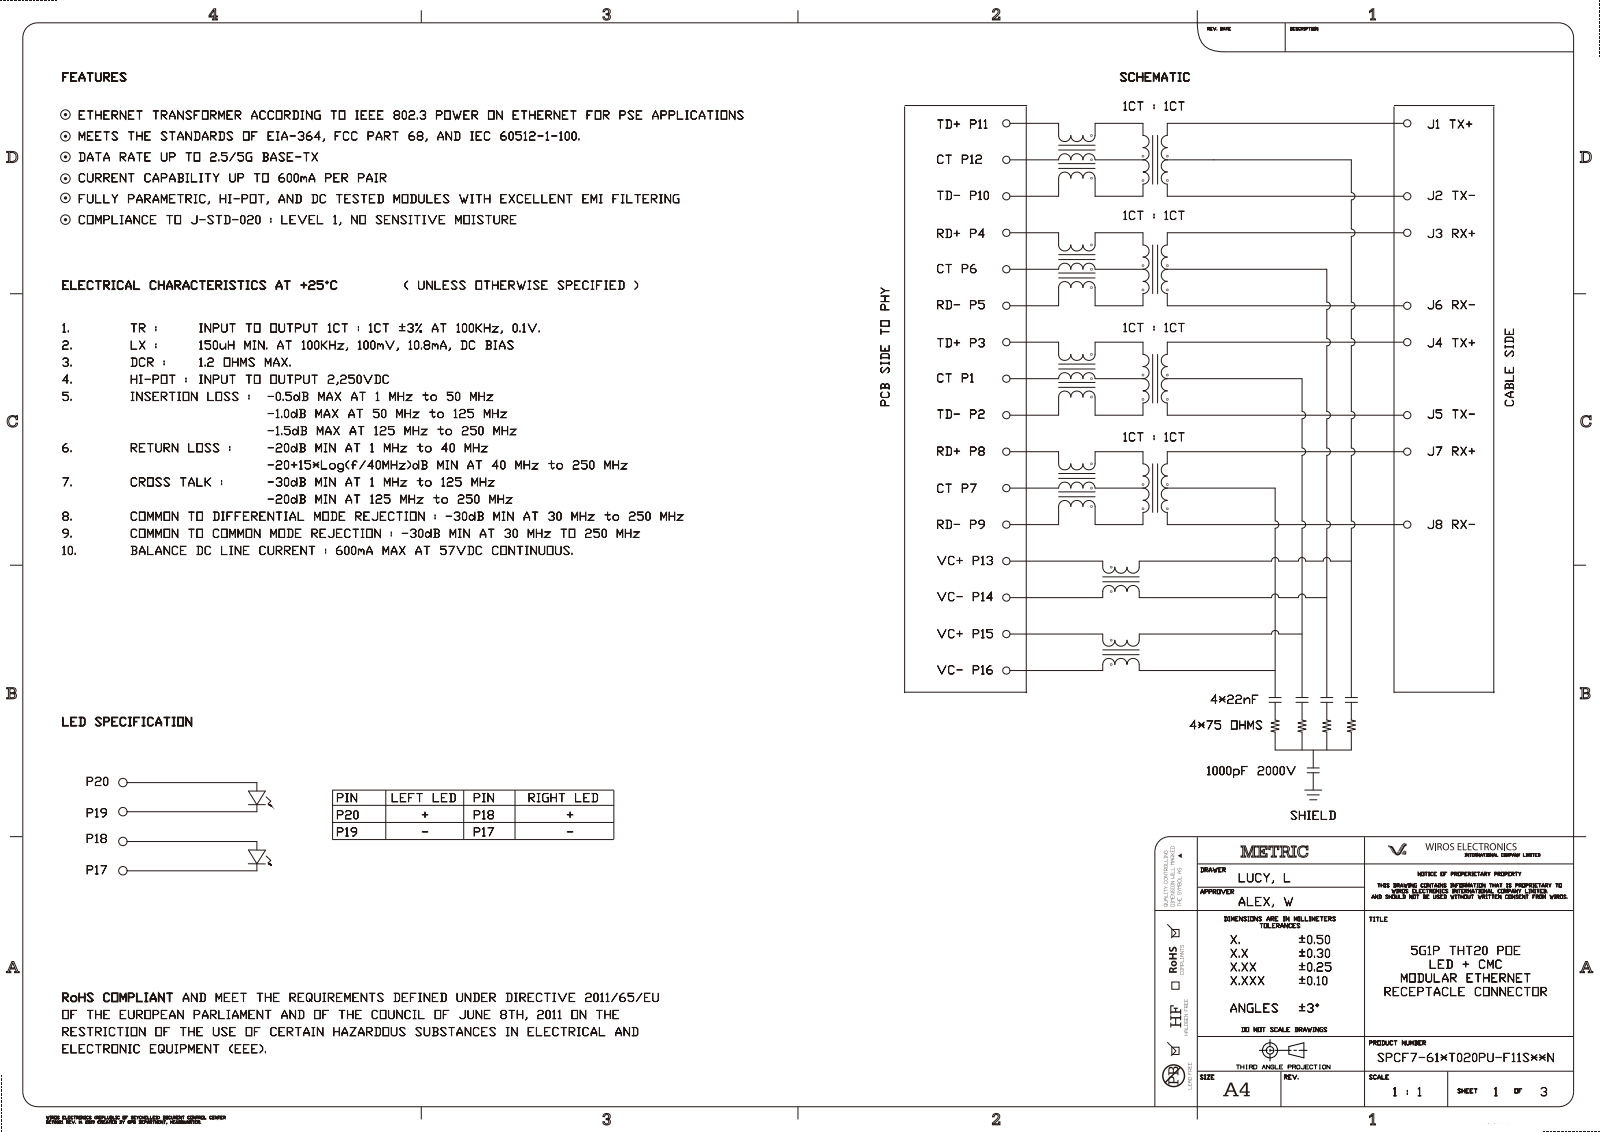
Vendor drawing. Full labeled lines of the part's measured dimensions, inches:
Part name (STEP PRODUCT): DIP_PIN_13; DIP_PIN_7; DIP_PIN_1; DIP_PIN_6 (+8 more)
STEP written by: SolidWorks 2016 (AUTOMOTIVE_DESIGN)
Units: inches
Bodies: 21 solids, 2548 faces (1655 planar, 813 cylindrical, 80 other)
Overall size (bounding box): 1.28 × 0.78 × 0.74
Volume: 0.206 in³ · Surface area: 16.59 in²
Round holes (diameter × count): ⌀0.059 ×1
Partial cylindrical surfaces — rounded edges, fillets, slot ends (radius × count): R0.006 ×200, R0.008 ×177, R0.011 ×48, R0.012 ×28, R0.016 ×23, R0.014 ×14, R0.053 ×8, R0.039 ×7
Main face-to-face distances: 0.031, 0.049, 0.041, 0.642, 0.64, 0.632, 0.134, 0.039, 0.593, 0.6
